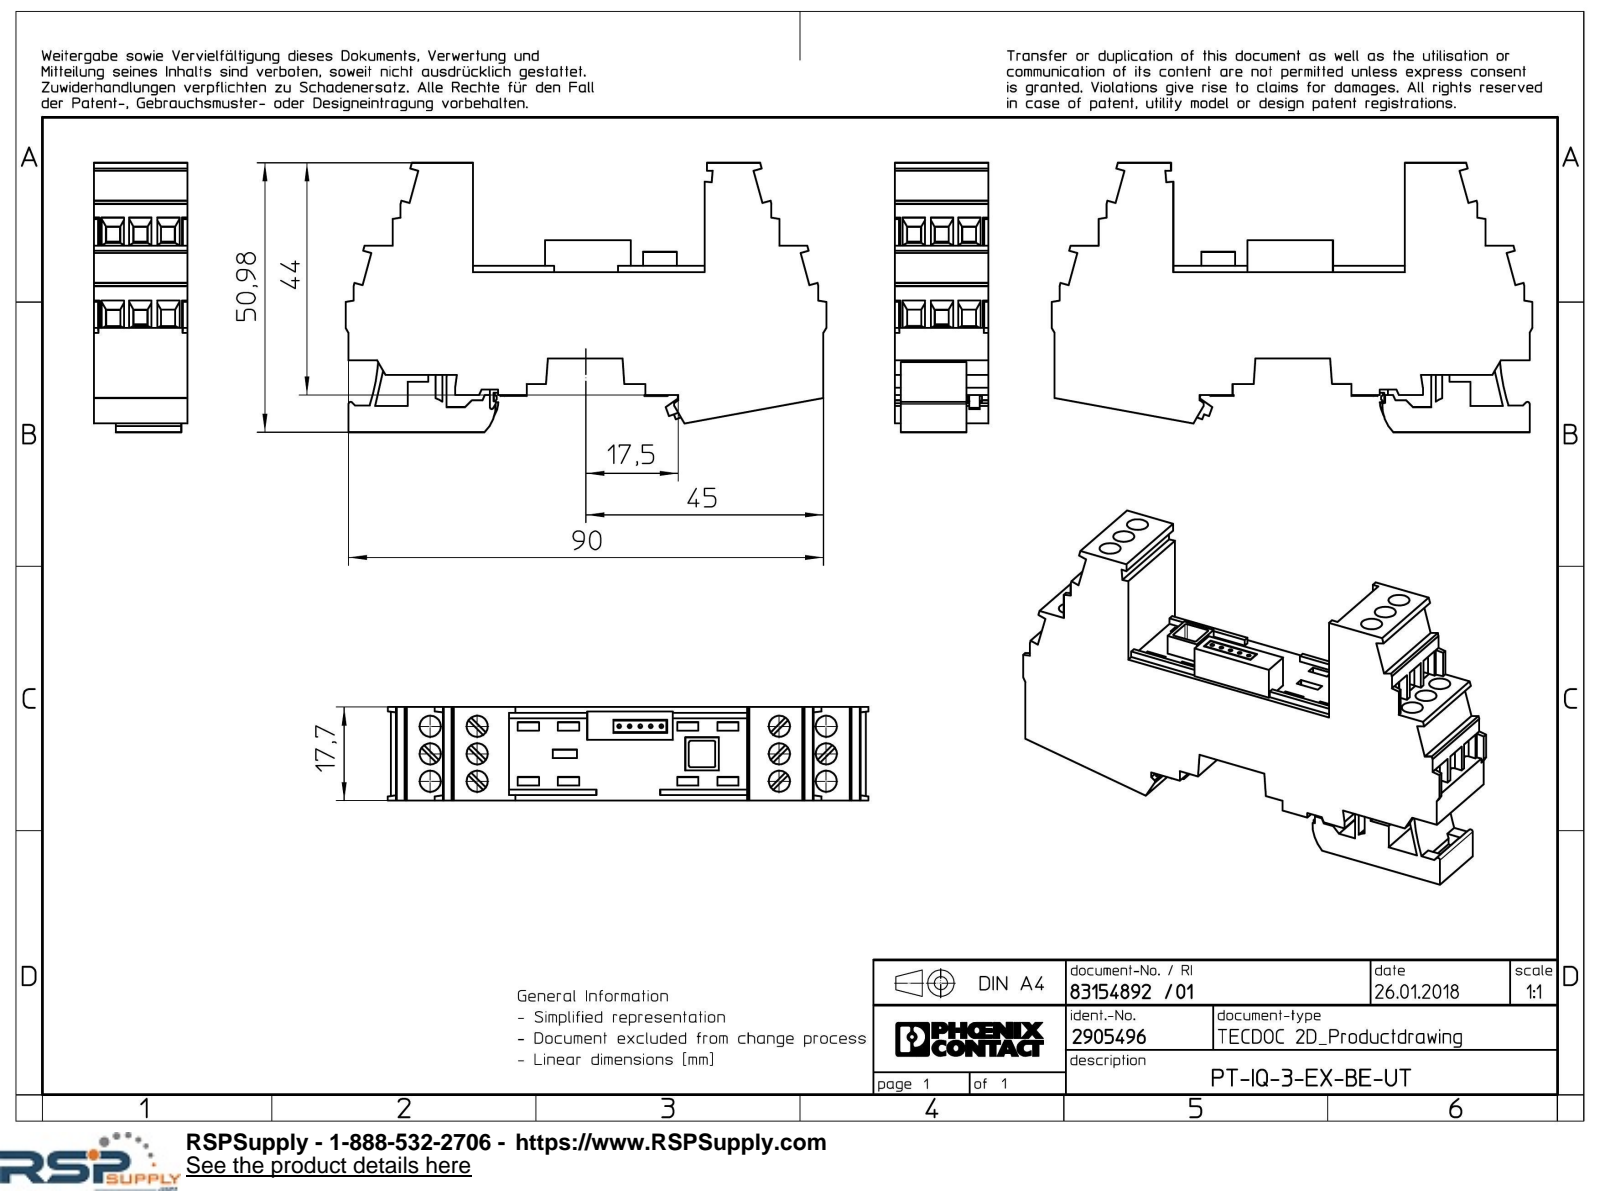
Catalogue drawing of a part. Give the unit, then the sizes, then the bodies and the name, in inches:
Units: inches
Overall size (bounding box): 3.585 × 2.007 × 0.697
Round holes (diameter × count): ⌀0.157 ×12, ⌀0.028 ×5
Partial cylindrical surfaces — rounded edges, fillets, slot ends (radius × count): R0.012 ×5, R0.016 ×1, R0.157 ×1, R0.374 ×1, R1.434 ×1
Main face-to-face distances: 0.697, 0.122, 1.192, 0.083, 0.643, 1.776, 2.007, 0.815, 0.177, 0.15
Hole centre spacings: 0.205, 0.406, 2.61, 0.35, 2.602, 0.079, 0.409, 0.539
Volume: 2.736 in³ · Surface area: 24.23 in²
Bodies: 1 solid, 617 faces (571 planar, 45 cylindrical, 1 other)
Part name (STEP PRODUCT): PT_IQ...EX_BE_UT-select
STEP written by: Creo Elements/Direct Modeling 20.1A 29-Sep-2018 (C) Parametric Technology GmbH (AUTOMOTIVE_DESIGN)
